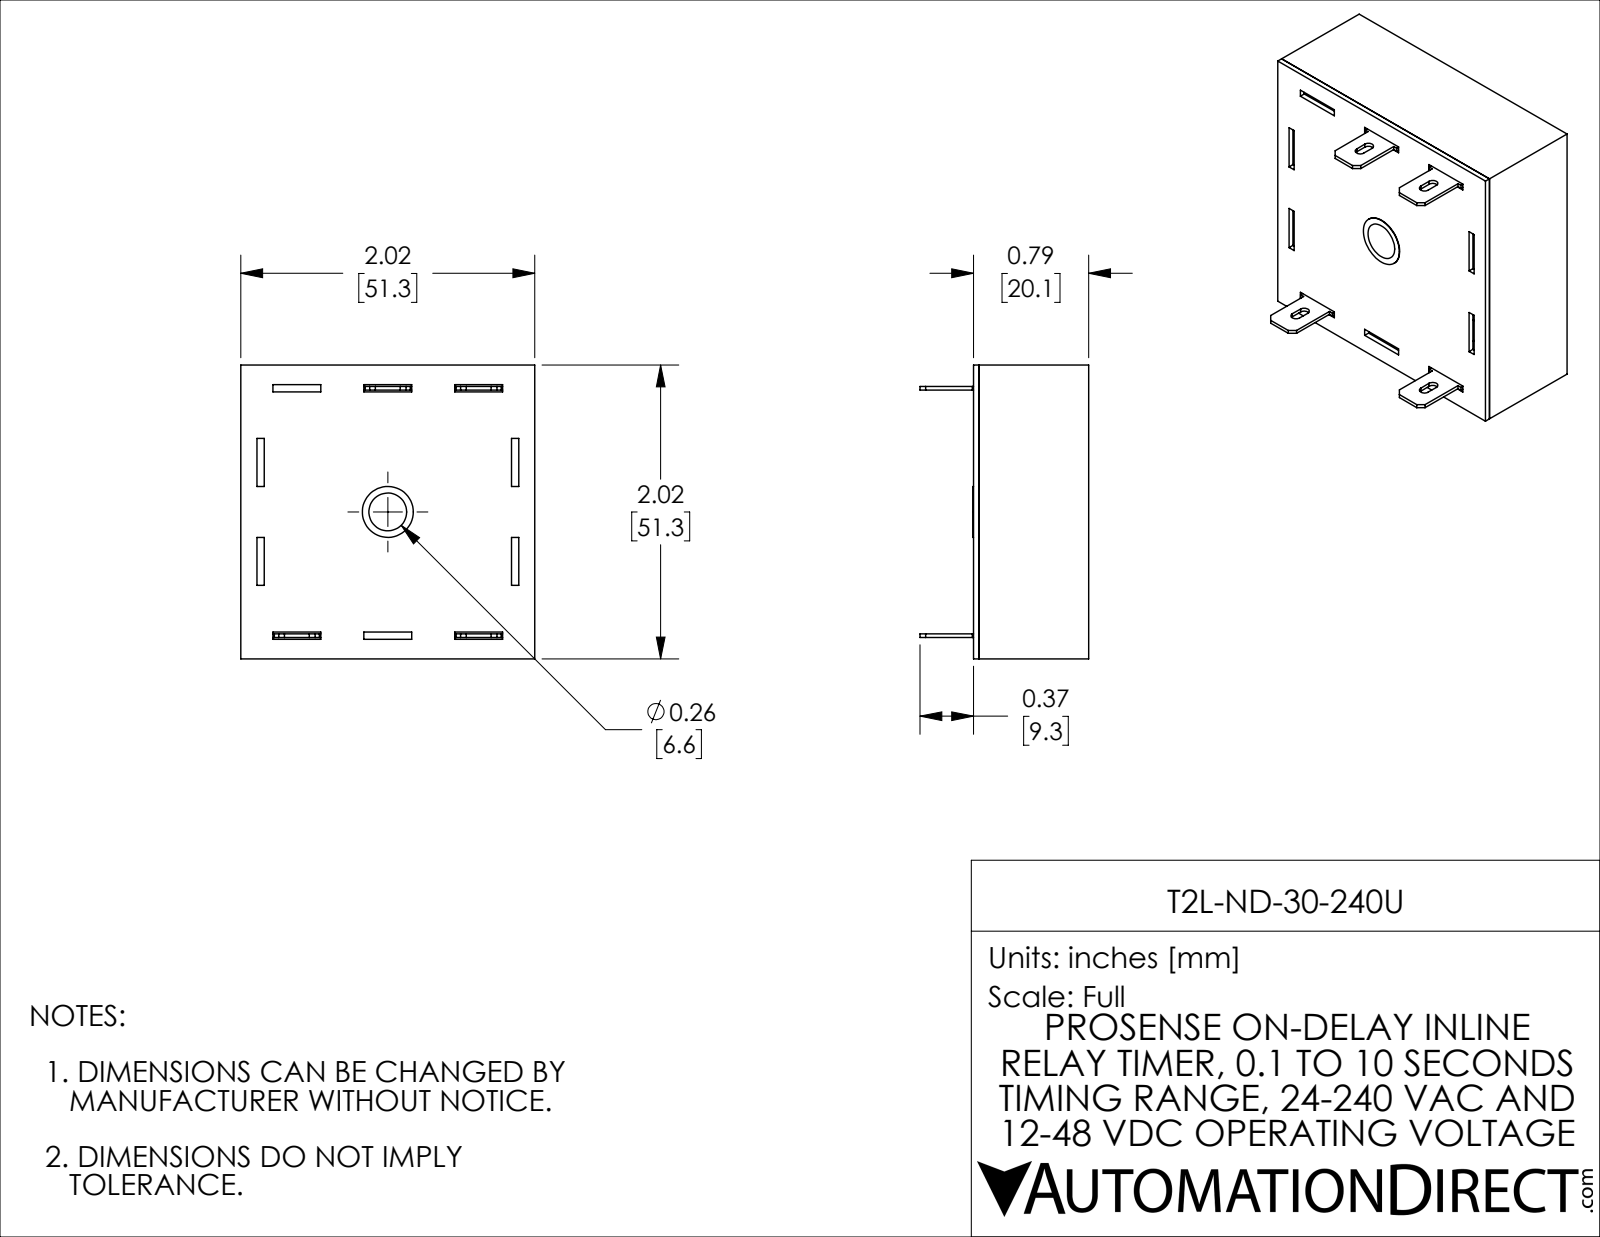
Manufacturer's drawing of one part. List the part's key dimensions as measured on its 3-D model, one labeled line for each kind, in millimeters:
Part name (STEP PRODUCT): T2L-ND-30-240U
STEP written by: SolidWorks 2021 (CONFIG_CONTROL_DESIGN)
Units: millimetres
Bodies: 6 solids, 160 faces (146 planar, 12 cylindrical, 2 other)
Overall size (bounding box): 51.31 × 51.31 × 29.46
Volume: 10 499 mm³ · Surface area: 20 889 mm²
Round holes (diameter × count): ⌀8.89 ×1
Partial cylindrical surfaces — rounded edges, fillets, slot ends (radius × count): R0.89 ×6
Main face-to-face distances: 1.14, 50.16, 19.15, 20.12, 0.97, 18.01, 18.98, 51.3, 49.02, 43.18
